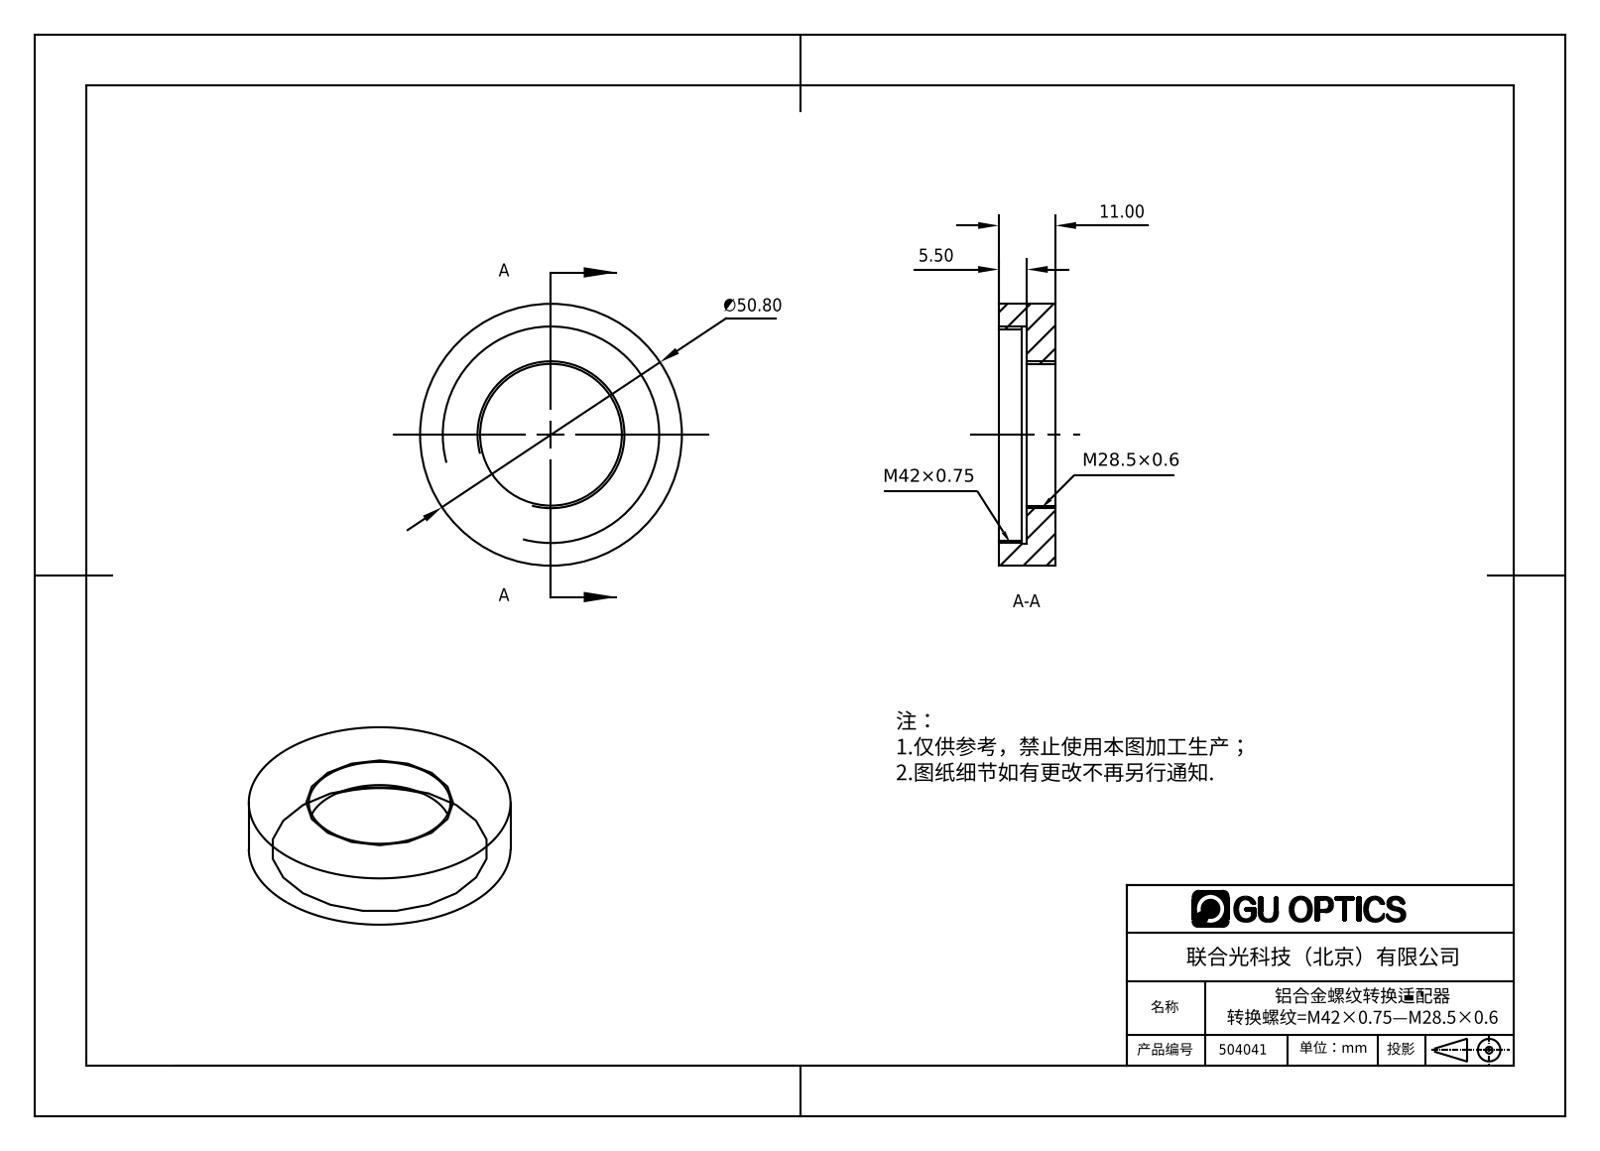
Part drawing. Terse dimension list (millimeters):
name: 504041
written by: SolidWorks 2016 (AUTOMOTIVE_DESIGN)
unit: mm
bodies: 1 solid, 12 faces (4 planar, 8 cylindrical, 0 other)
size: 50.8 × 50.8 × 11
volume: 11 689 mm³; area: 5 965 mm²
holes: 1× ⌀27.5, 1× ⌀41, 1× ⌀42.2
bosses: 1× ⌀50.8
face distances: 5.5, 11, 4.5, 1, 6.5
